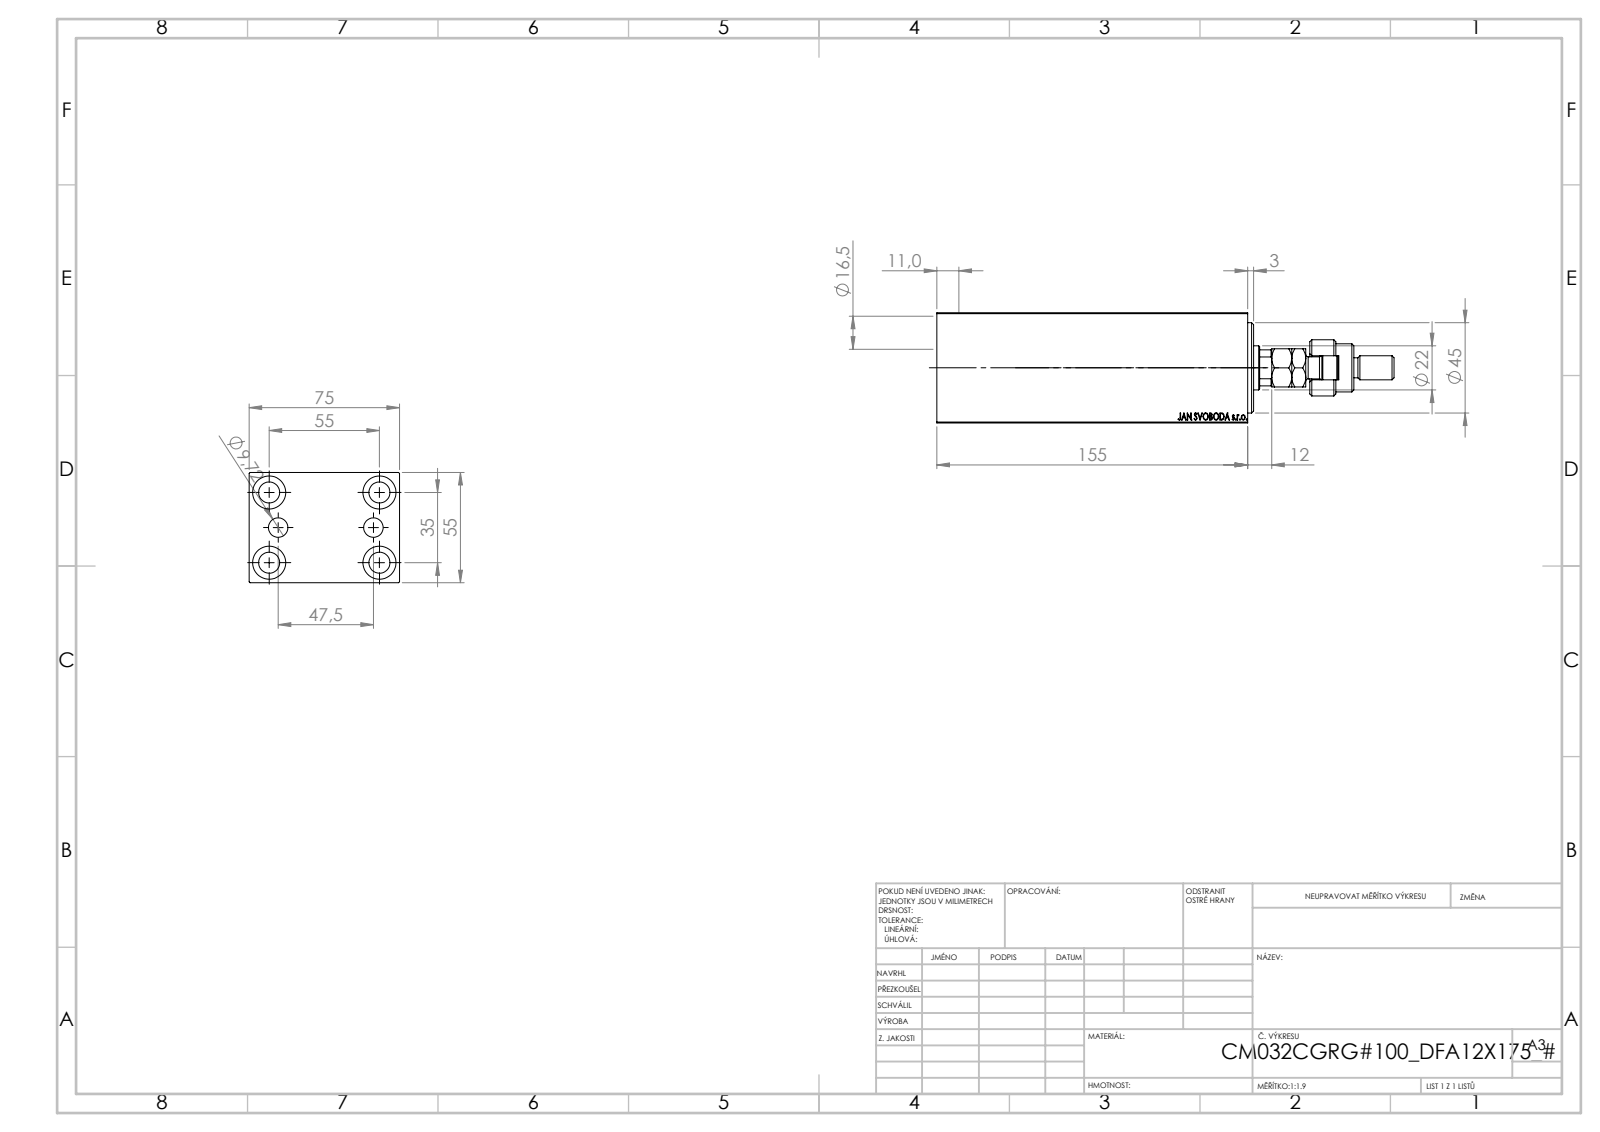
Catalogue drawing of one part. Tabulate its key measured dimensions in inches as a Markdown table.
| quantity | value |
| --- | --- |
| part name | V450CM_C_VCP; MFA; V450CM_C_Body; V450CM_VC_B (+1 more) |
| STEP written by | SolidWorks 2019 (CONFIG_CONTROL_DESIGN) |
| units | inches |
| bodies | 5 solids, 943 faces (436 planar, 69 cylindrical, 438 other) |
| overall size | 8.976 × 2.953 × 2.165 |
| volume | 33.6 in³ |
| surface area | 172.3 in² |
| round holes (diameter × count) | 0.413 × 5, 0.65 × 4, 0.157 × 2, 0.383 × 2, 0.866 × 1, 1.004 × 1, 1.26 × 1, 1.339 × 1, 1.772 × 1 |
| round bosses / shafts (diameter × count) | 1.102 × 1, 0.945 × 1, 0.709 × 1, 0.472 × 1, 0.433 × 1, 0.394 × 1 |
| partial cylindrical surfaces (radius × count) | 0.384 × 1, 0.413 × 1 |
| main face-to-face distances | 2.165, 2.953, 0.197, 6.102, 1.132, 4.97, 0.315, 4.774, 5.906, 0.118 |
| hole center spacings | 0.705, 1.283, 2.132, 0.935, 1.378, 2.165, 2.567, 1.87 |
